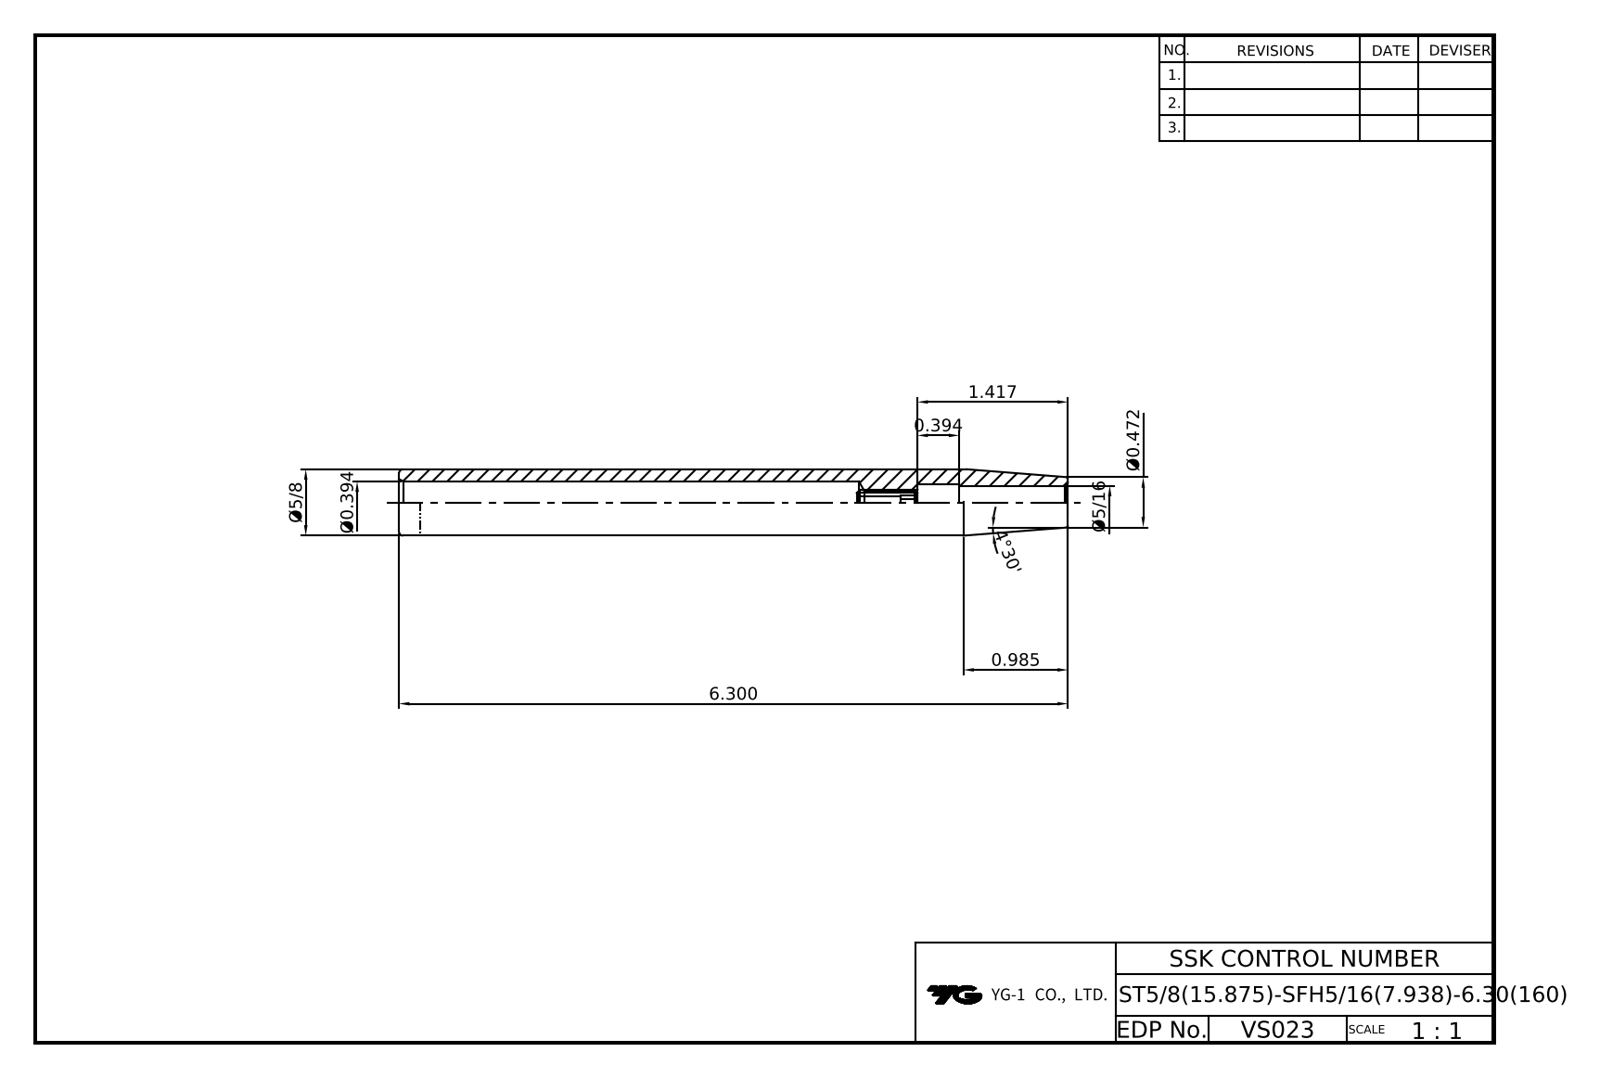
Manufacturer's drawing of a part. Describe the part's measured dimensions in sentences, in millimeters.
The part is named "ST15_875-SFH7_9375-160". Its 3-D file was written by "CREO PARAMETRIC BY PTC INC, 2018500 (CONFIG_CONTROL_DESIGN)". It is 1 solid with 32 faces: 4 planar, 10 cylindrical and 18 other. Overall it measures 160 by 15.88 by 15.88 millimeters. Its volume is 19 516 cubic millimeters and its surface area 12 709 square millimeters. Round holes: 1 of diameter 6.06, 1 of diameter 8, 1 of diameter 8.6, 1 of diameter 10.06. Round bosses or shafts: 1 of diameter 15.88. The main face-to-face distances are 124, 160, 36, 134, 10, 26.
